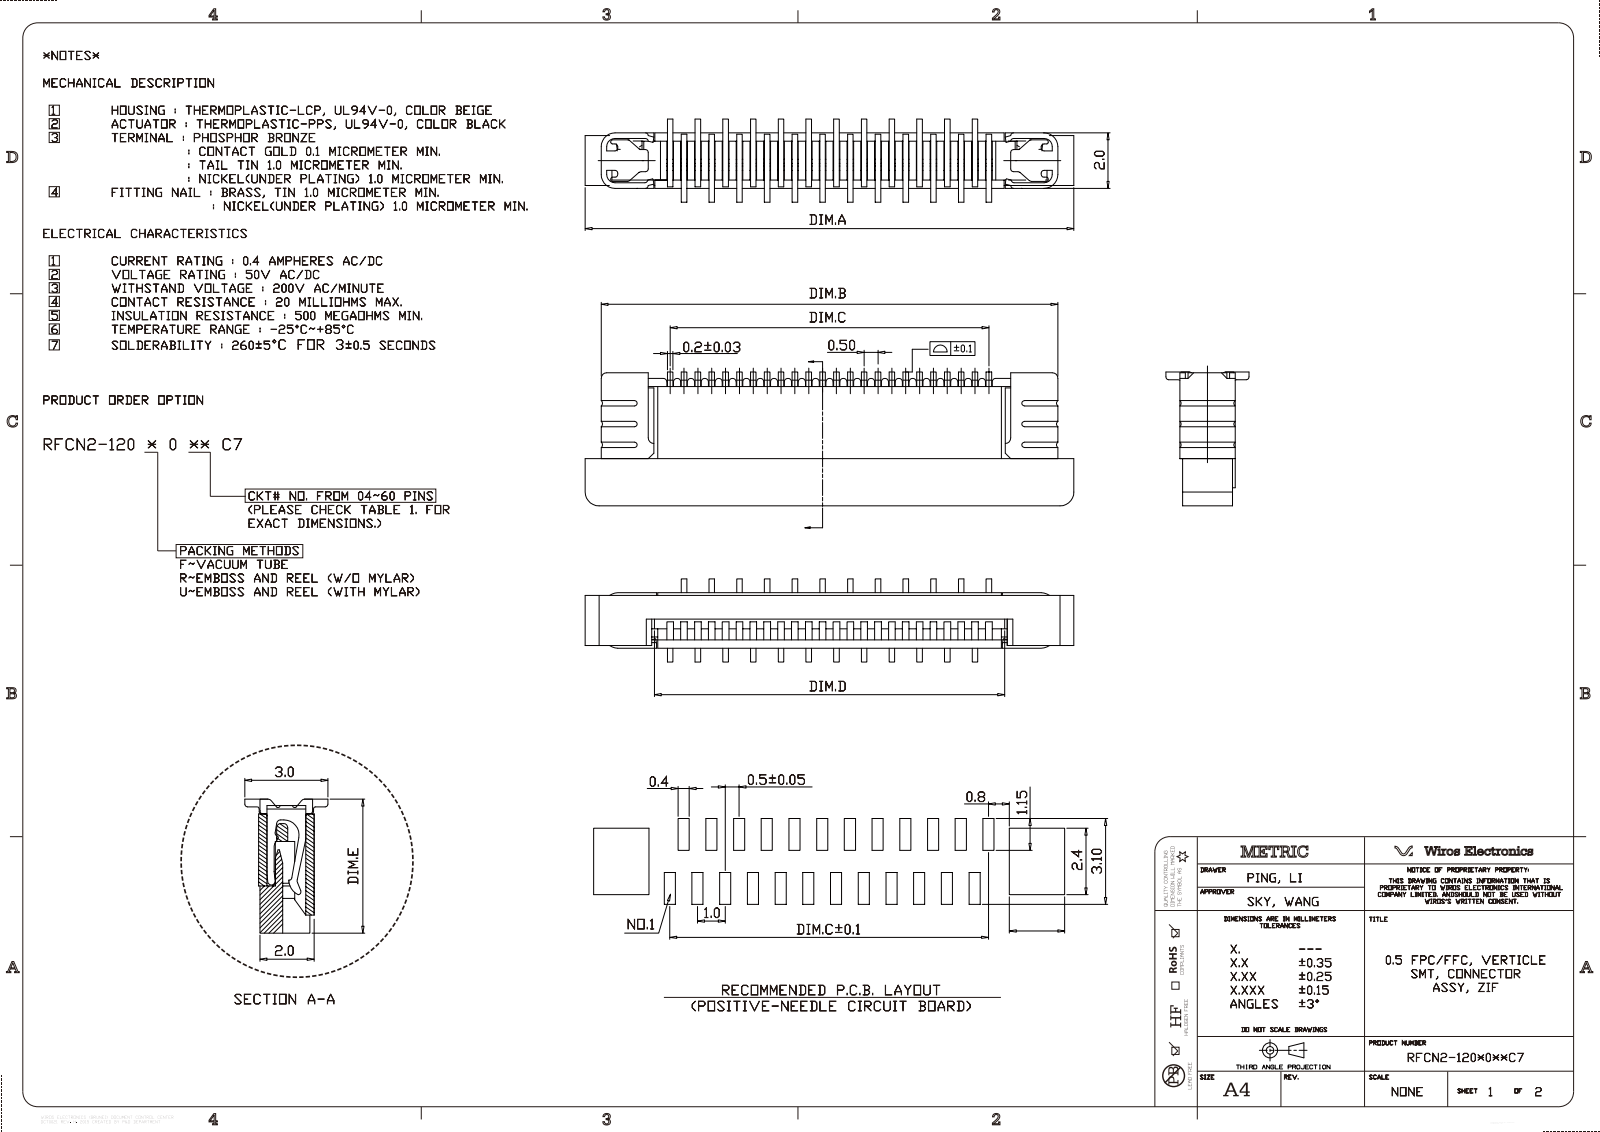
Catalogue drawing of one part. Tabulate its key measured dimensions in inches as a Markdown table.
| quantity | value |
| --- | --- |
| part name | FPC; FPC-1; FPC-2; FPC-3 (+1 more) |
| STEP written by | PRO/ENGINEER BY PARAMETRIC TECHNOLOGY CORPORATION, 2010430 (CONFIG_CONTROL_DESIGN) |
| units | inches |
| bodies | 8 solids, 684 faces (292 planar, 268 cylindrical, 124 other) |
| overall size | 0.299 × 0.173 × 0.118 |
| volume | 0.002 in³ |
| surface area | 0.425 in² |
| partial cylindrical surfaces (radius × count) | 0.004 × 43, 0.008 × 16, 0.012 × 10, 0.02 × 8, 0.029 × 8, 0.008 × 4, 0.01 × 4, 0.01 × 2 |
| main face-to-face distances | 0.039, 0.031, 0.02, 0.045, 0.071, 0.053, 0.024, 0.026, 0.014, 0.079 |
